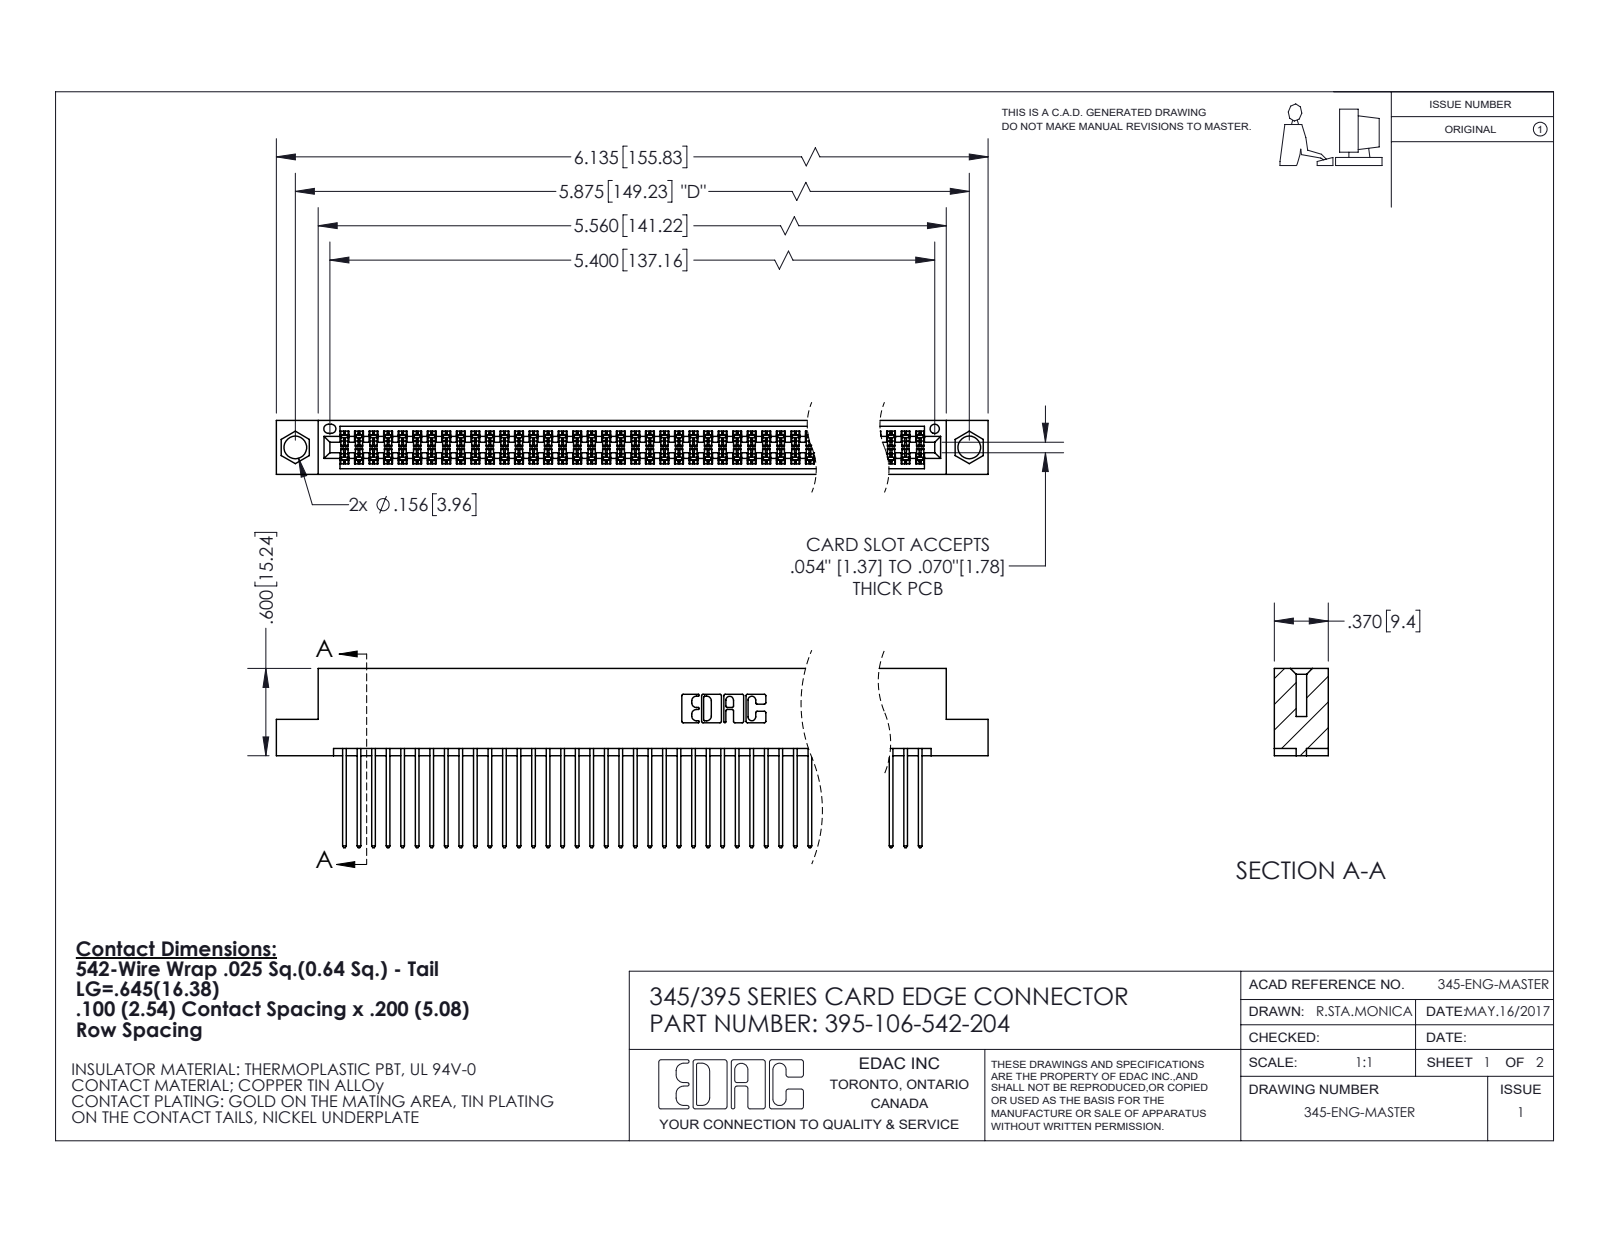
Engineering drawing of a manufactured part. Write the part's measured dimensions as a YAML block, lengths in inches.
part_name: "345-292-001_345-293-142; 395-106-542-204; 345 Part_Flush Mounting Lugs - 0.156 Dia-TI"
step_written_by: "SolidWorks 2020 (CONFIG_CONTROL_DESIGN)"
units: inches
bodies: {solids: 107, faces: 5440, planar: 3592, cylindrical: 1848, other: 0}
overall_size: [6.135, 1.232, 0.37]
volume: 0.954
surface_area: 39.49
round_holes:
  - {diameter: 0.156, count: 2}
  - {diameter: 0.064, count: 1}
partial_cylinders:
  - {radius: 0.006, count: 159}
  - {radius: 0.01, count: 106}
  - {radius: 0.01, count: 22}
  - {radius: 0.007, count: 6}
  - {radius: 0.031, count: 6}
  - {radius: 0.026, count: 3}
  - {radius: 0.014, count: 2}
  - {radius: 0.019, count: 2}
face_to_face_distances: [0.298, 0.072, 0.2, 0.098, 0.272, 0.025, 0.225, 0.37, 0.175, 0.149]
hole_center_spacings: [0.27, 5.639, 5.875]
